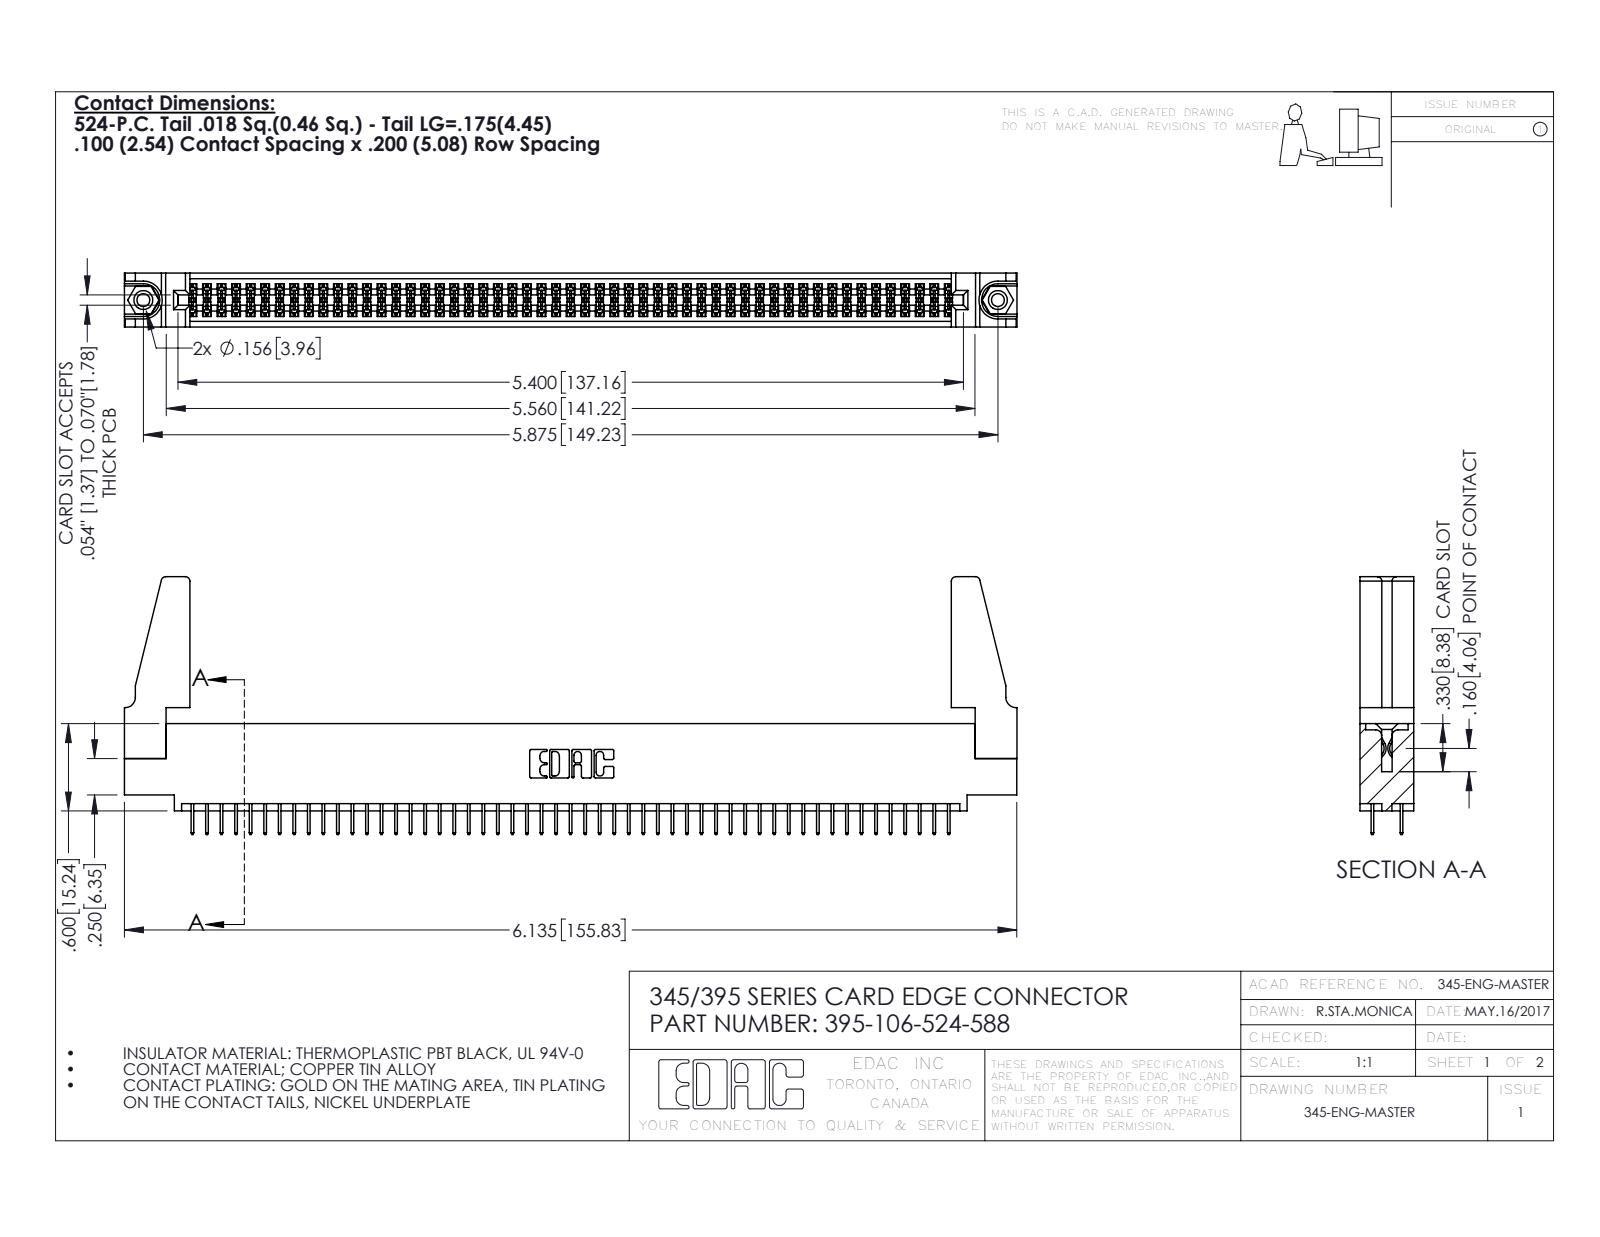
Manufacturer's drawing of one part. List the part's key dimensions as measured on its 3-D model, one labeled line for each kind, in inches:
Part name (STEP PRODUCT): 395-106-524-588; 345-292-001_345-293-124; 345-250-001_345-250-001-102; 345-220-078_345-220-088 (+1 more)
STEP written by: SolidWorks 2016 (CONFIG_CONTROL_DESIGN)
Units: inches
Bodies: 111 solids, 5978 faces (4290 planar, 1672 cylindrical, 16 other)
Overall size (bounding box): 6.136 × 1.772 × 0.37
Volume: 1.114 in³ · Surface area: 39.04 in²
Round holes (diameter × count): ⌀0.089 ×2, ⌀0.125 ×2, ⌀0.156 ×2, ⌀0.064 ×1
Round bosses / shafts (diameter × count): ⌀0.155 ×2
Partial cylindrical surfaces — rounded edges, fillets, slot ends (radius × count): R0.006 ×159, R0.01 ×22, R0.03 ×8, R0.007 ×6, R0.031 ×6, R0.026 ×3, R0.014 ×2, R0.019 ×2
Main face-to-face distances: 0.072, 0.298, 0.37, 0.2, 0.098, 0.272, 0.025, 0.225, 0.072, 0.175
Hole centre spacings: 0.27, 5.639, 5.875
